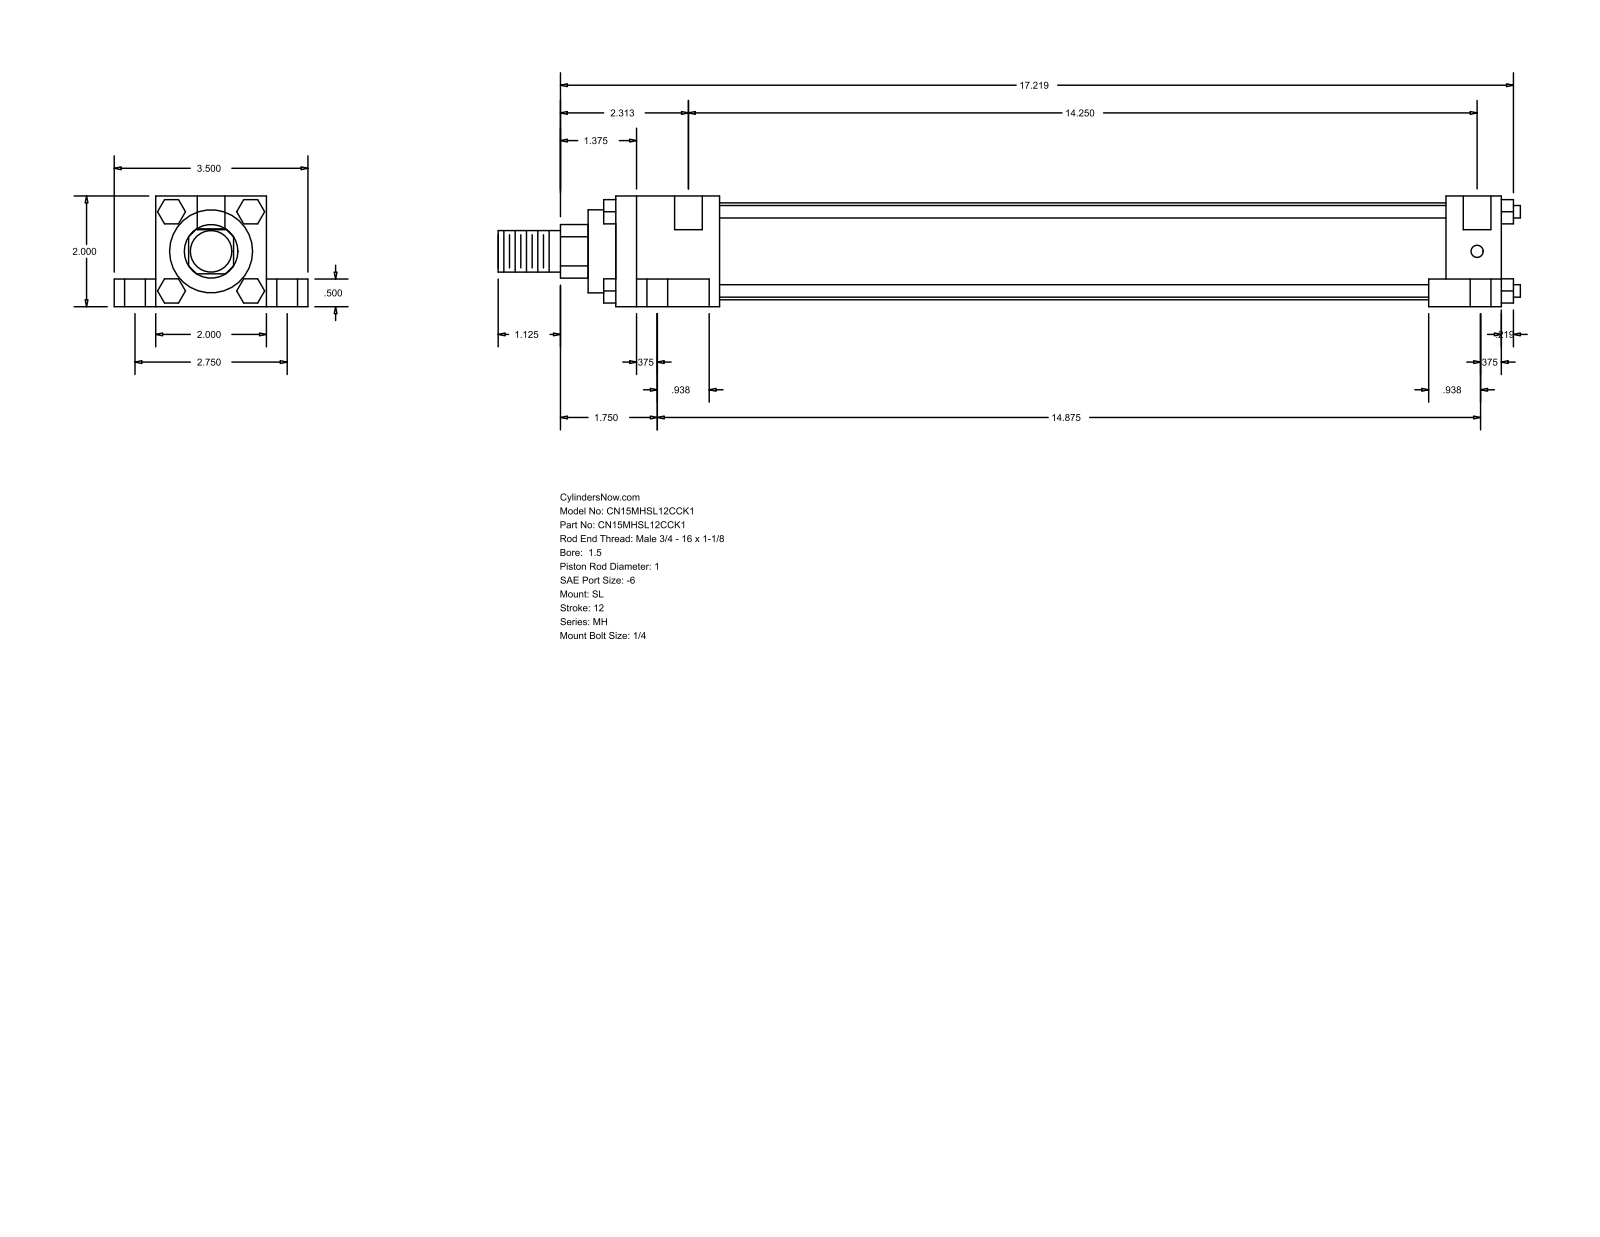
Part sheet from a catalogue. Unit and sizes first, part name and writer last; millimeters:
Units: millimetres
Overall size (bounding box): 469.11 × 88.9 × 50.8
Round holes (diameter × count): ⌀5.56 ×4, ⌀9.53 ×4, ⌀15.88 ×4, ⌀12.7 ×2
Round bosses / shafts (diameter × count): ⌀5.71 ×4, ⌀44.45 ×1, ⌀38.1 ×1, ⌀25.4 ×1, ⌀19.05 ×1
Partial cylindrical surfaces — rounded edges, fillets, slot ends (radius × count): R12.29 ×1
Main face-to-face distances: 50.8, 12.7, 38.1, 19.05, 69.85, 406.4, 25.4, 9.52, 33.34, 363.54
Hole centre spacings: 34.96, 36.64, 37.73, 69.84, 365.13, 365.2, 368.37, 377.82
Bodies: 0 solids, 148 faces (112 planar, 36 cylindrical, 0 other)
Part name (STEP PRODUCT): MH_SL__0150_1
STEP written by: GSSL Pune (CONFIG_CONTROL_DESIGN)
